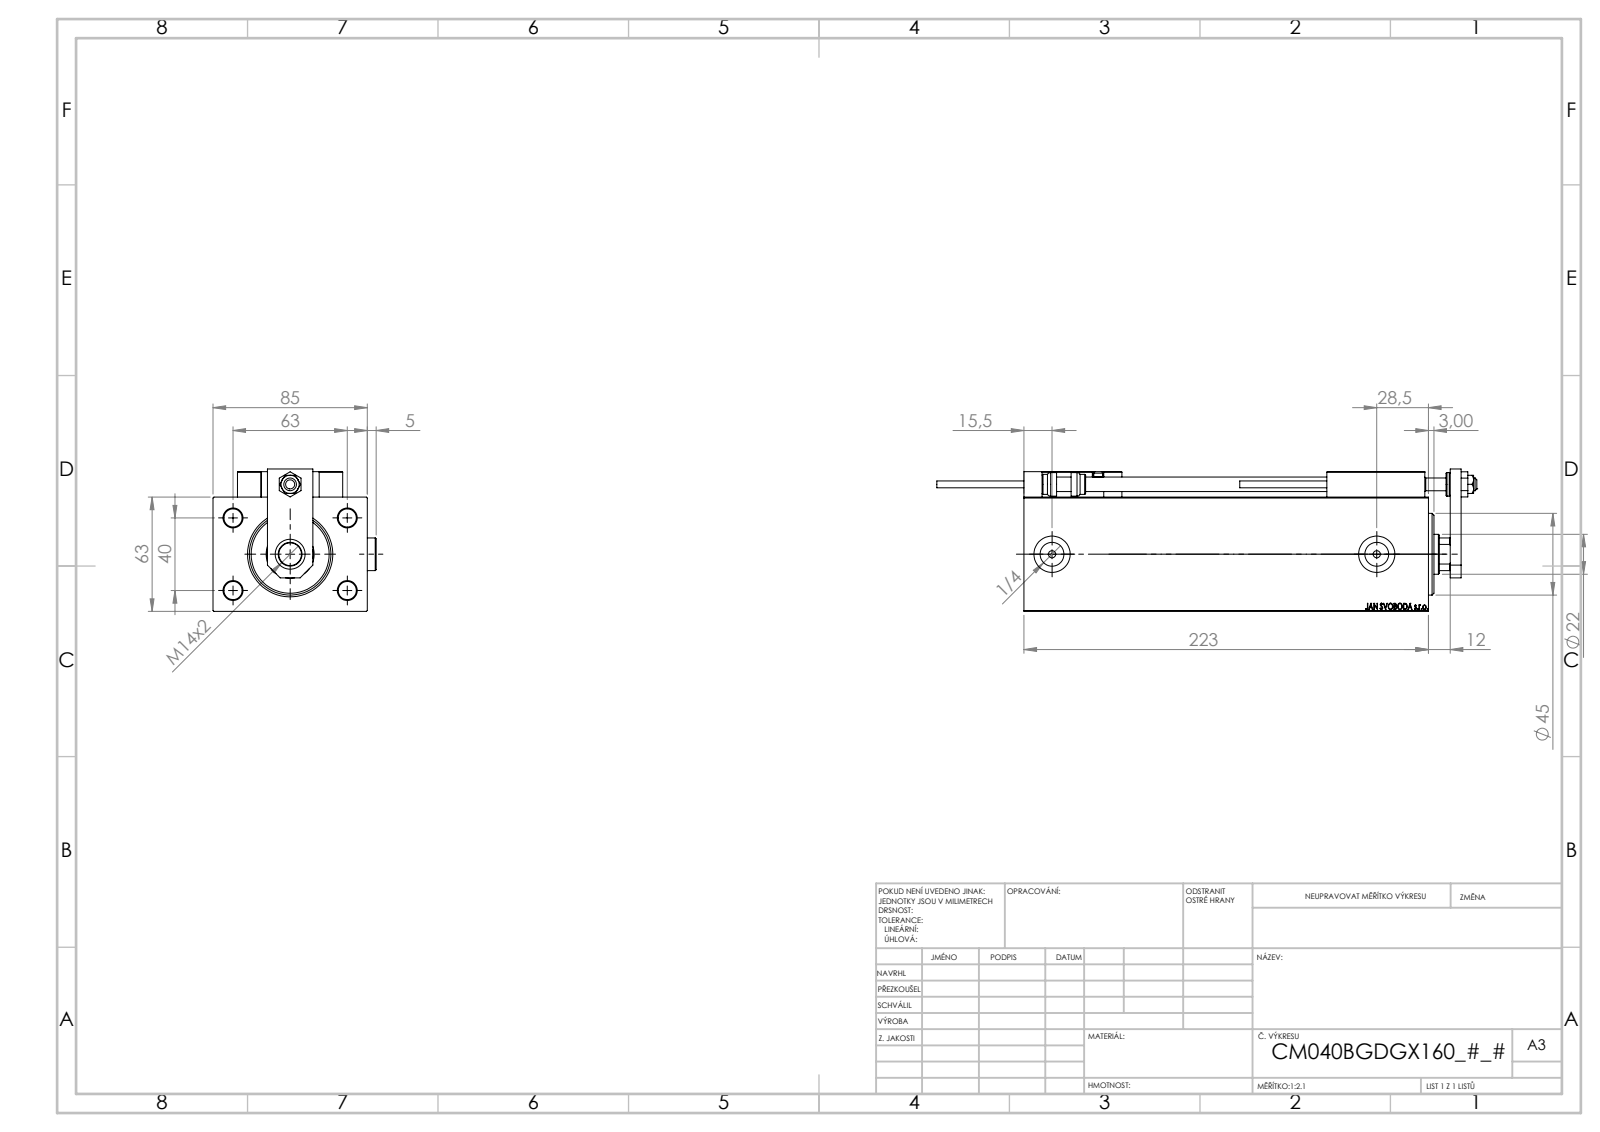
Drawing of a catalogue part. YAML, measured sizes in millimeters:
part_name: "SWITCH_X_FRONT_BACK; ALLEN BOLT D8; Block; NUT_D10 (+7 more)"
step_written_by: "SolidWorks 2019 (CONFIG_CONTROL_DESIGN)"
units: millimeters
bodies: {solids: 26, faces: 1372, planar: 595, cylindrical: 200, other: 577}
overall_size: [297.7, 89.9, 78.5]
volume: 1096000
surface_area: 167041
round_holes:
  - {diameter: 4, count: 6}
  - {diameter: 8, count: 5}
  - {diameter: 3.2, count: 4}
  - {diameter: 10, count: 4}
  - {diameter: 5, count: 2}
  - {diameter: 13.16, count: 2}
  - {diameter: 20, count: 2}
  - {diameter: 7, count: 1}
  - {diameter: 12.5, count: 1}
  - {diameter: 16.5, count: 1}
  - {diameter: 22, count: 1}
  - {diameter: 25.5, count: 1}
round_bosses_or_shafts:
  - {diameter: 18, count: 2}
  - {diameter: 5, count: 2}
  - {diameter: 3.8, count: 2}
  - {diameter: 13, count: 1}
  - {diameter: 11, count: 1}
partial_cylinders:
  - {radius: 0.3, count: 30}
  - {radius: 3, count: 2}
  - {radius: 10.5, count: 1}
face_to_face_distances: [63, 85, 12, 223, 211, 14, 77, 18, 30, 13.5]
hole_center_spacings: [37.31, 11.37, 20, 29.59, 29.69, 36.06, 36.53, 40]
